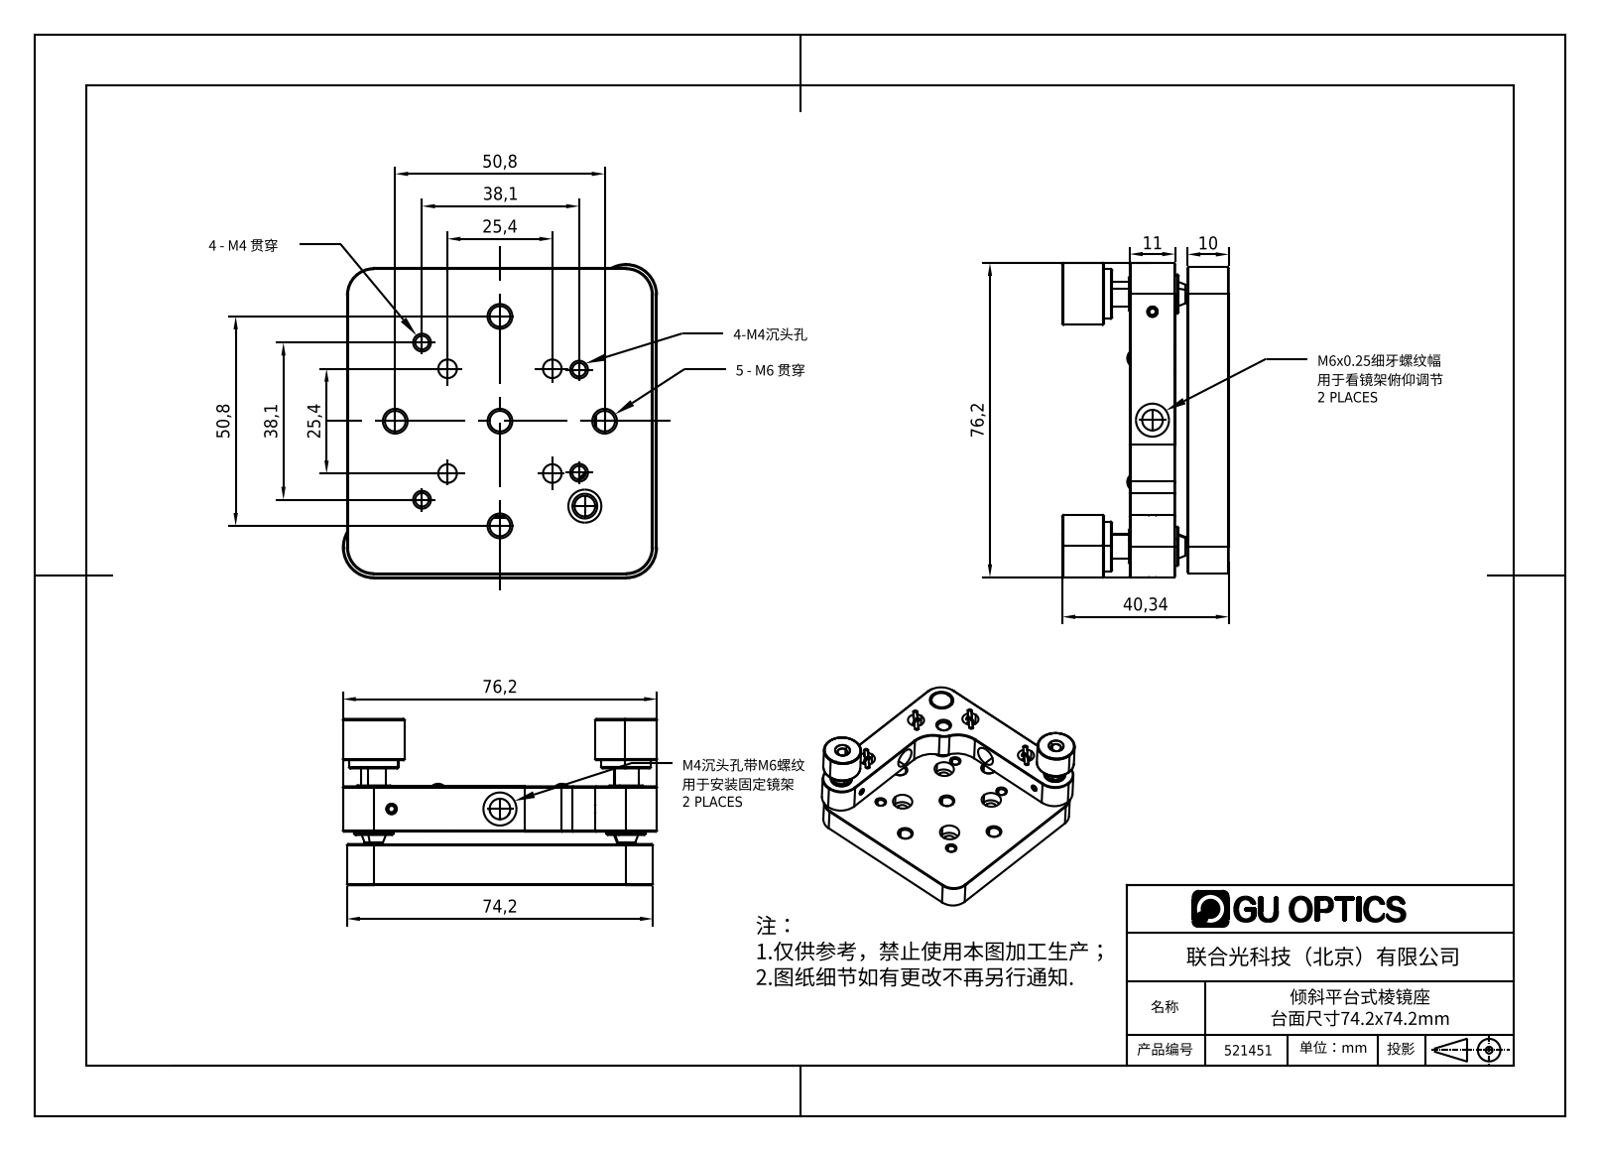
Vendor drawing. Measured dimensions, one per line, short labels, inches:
name: 1.1.sldasm-Part-3; 1.1; 1.1.sldasm-Part-5; 1.1.sldasm-Part-1 (+2 more)
written by: SolidWorks 2020 (CONFIG_CONTROL_DESIGN)
unit: in
bodies: 4 solids, 397 faces (123 planar, 0 cylindrical, 274 other)
size: 3 × 3 × 1.588
face distances: 0.394, 0.551, 0.945, 0.512, 0.433, 0.118, 0.039, 2.961, 2.921, 0.591
